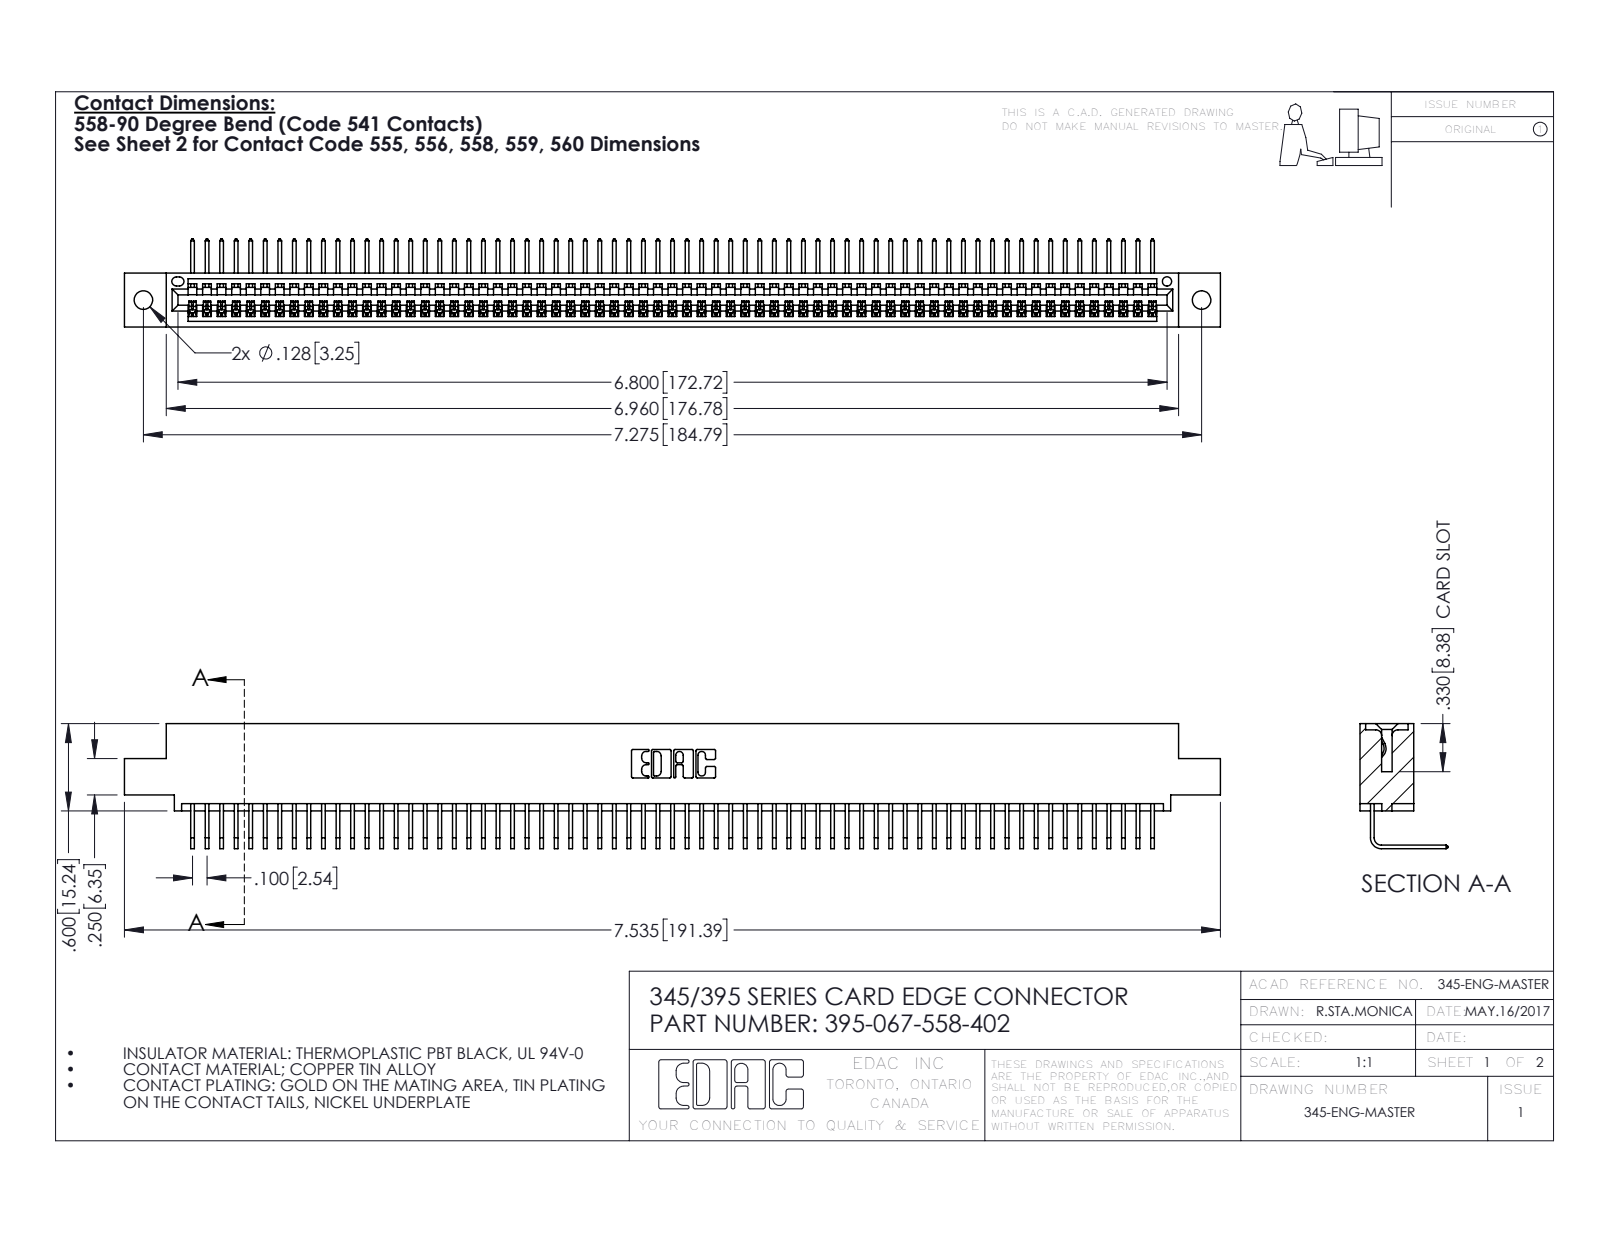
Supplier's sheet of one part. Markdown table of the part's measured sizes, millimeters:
| quantity | value |
| --- | --- |
| part name | 345 Part_0.110 Offset - 0.128 Dia; 345-292-001_558 Tail - 2; 395-067-558-402 |
| STEP written by | SolidWorks 2016 (CONFIG_CONTROL_DESIGN) |
| units | millimeters |
| bodies | 68 solids, 4150 faces (2898 planar, 1252 cylindrical, 0 other) |
| overall size | 191.4 × 21.8 × 15.4 |
| volume | 18 500 mm³ |
| surface area | 26 040 mm² |
| round holes (diameter × count) | 3.3 × 2, 1.6 × 1 |
| partial cylindrical surfaces (radius × count) | 0.2 × 134, 0.3 × 22, 0.2 × 6, 0.8 × 6, 0.7 × 3, 0.8 × 2, 1 × 2, 0.4 × 1 |
| main face-to-face distances | 1.8, 7.6, 9.4, 5.1, 2.5, 6.9, 0.6, 5.7, 3.8, 1.8 |
| hole center spacings | 6.9, 178.8, 184.8 |
